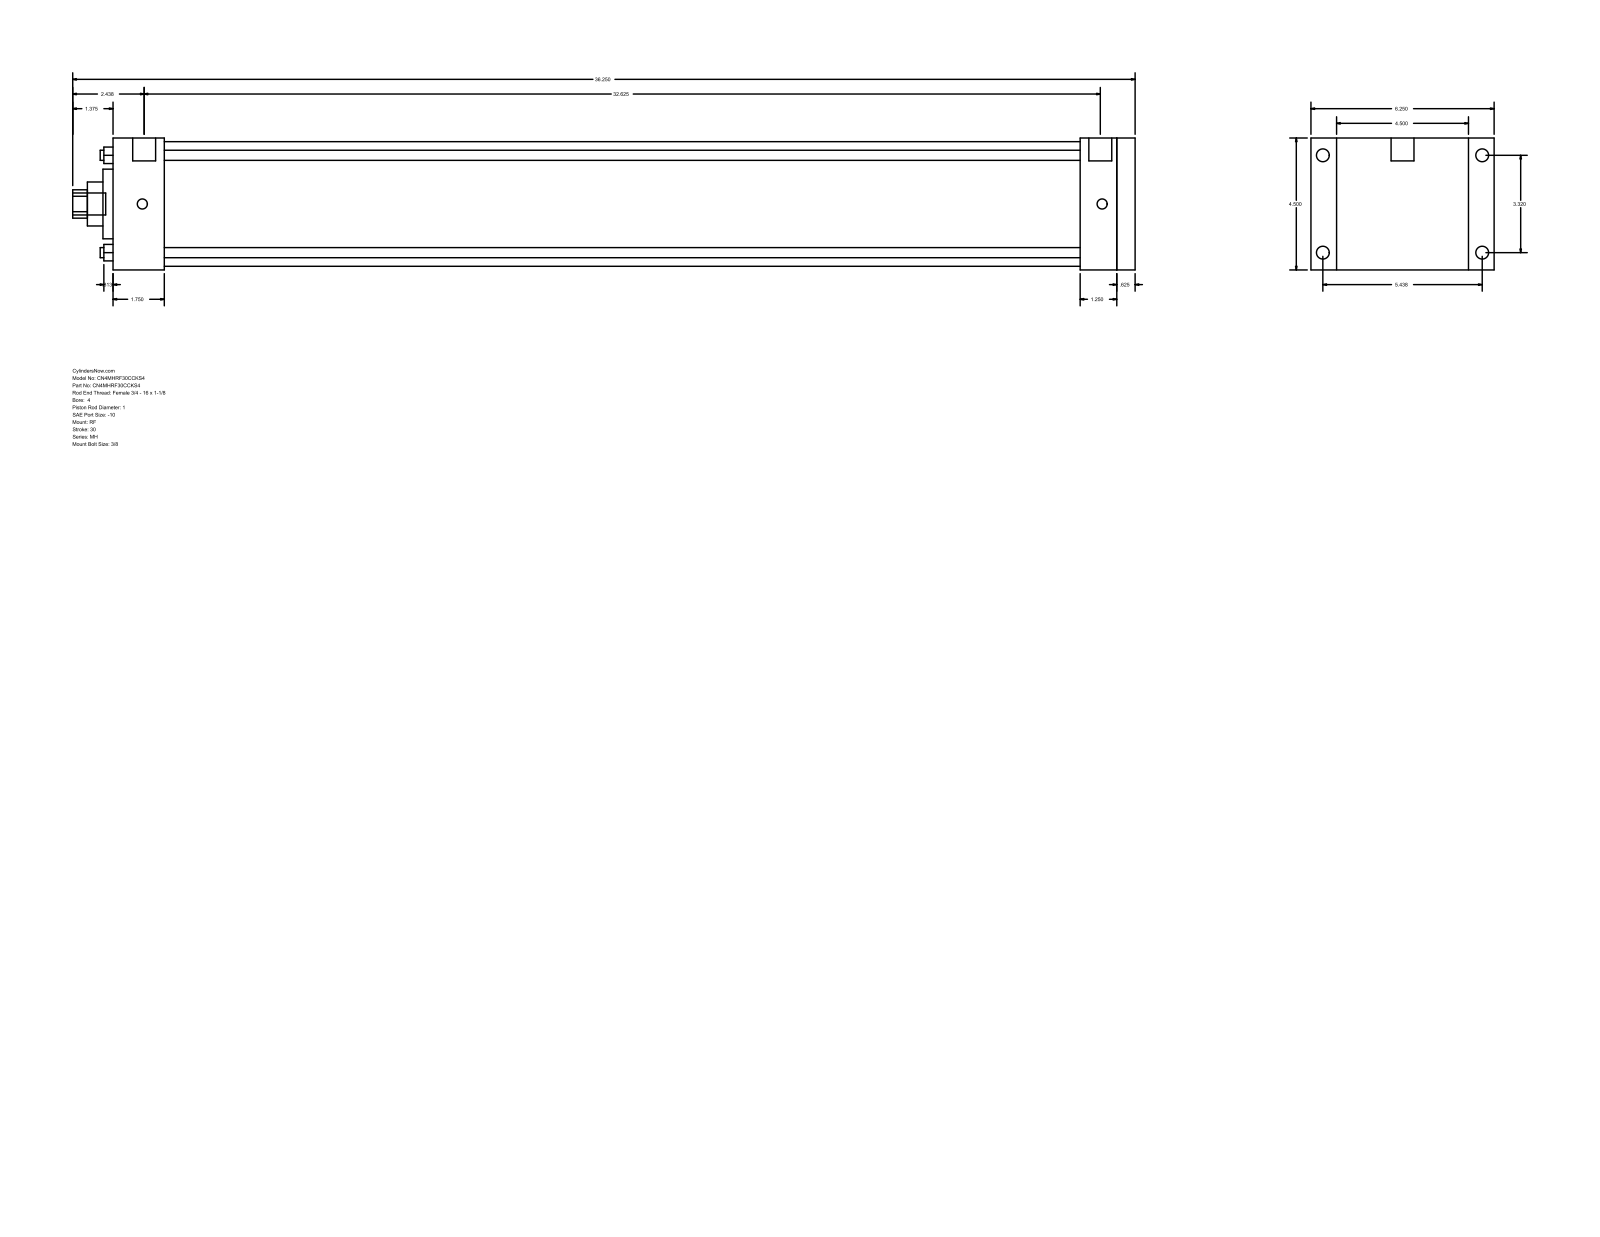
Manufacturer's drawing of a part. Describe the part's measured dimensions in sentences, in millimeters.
The part is named "MH_RF__0400_1". Its 3-D file was written by "GSSL Pune (CONFIG_CONTROL_DESIGN)". It is 0 solids with 94 faces: 65 planar, 29 cylindrical and 0 other. Overall it measures 920.75 by 158.75 by 114.3 millimeters. Round holes: 4 of diameter 8.76, 1 of diameter 25.4, 1 of diameter 38.1, 1 of diameter 60.33, 1 of diameter 107.95. Round bosses or shafts: 4 of diameter 11.13, 4 of diameter 8.73, 2 of diameter 19.84, 1 of diameter 19.05. Partial cylindrical surfaces (rounded edges, fillets, slot ends): 1 of radius 12.29. The main face-to-face distances are 114.3, 885.83, 15.87, 869.96, 47.63, 44.46, 825.5, 841.37, 838.2, 793.74. The hole center spacings are 59.62, 84.32, 119.25.
